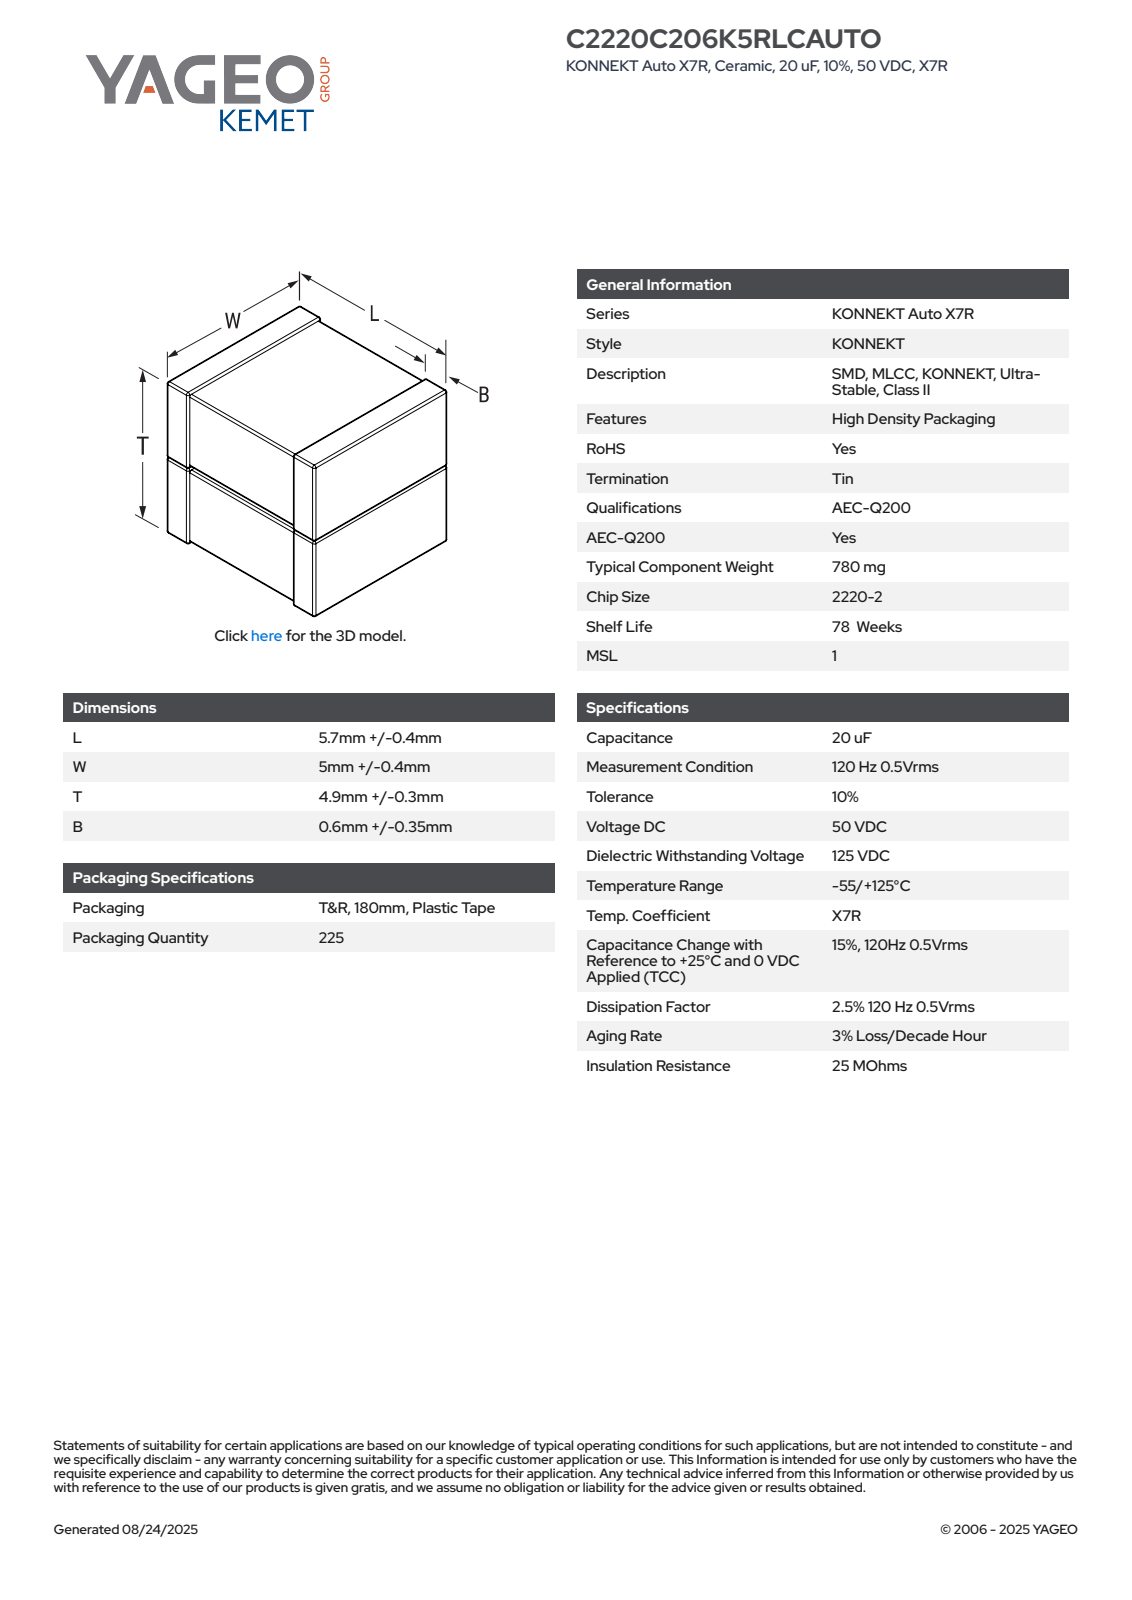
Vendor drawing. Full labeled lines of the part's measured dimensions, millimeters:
Part name (STEP PRODUCT): CCSS_K2T_2220-2_L6.1W5.4B0.95T5.2
STEP written by: SolidWorks 2020 (AUTOMOTIVE_DESIGN)
Units: millimetres
Bodies: 4 solids, 189 faces (81 planar, 76 cylindrical, 32 other)
Overall size (bounding box): 6.1 × 5.4 × 5.2
Volume: 162 mm³ · Surface area: 231 mm²
Main face-to-face distances: 2.46, 2.6, 6.1, 5.06, 5.26, 2.53, 2.67, 5.13, 5.33, 5.2
